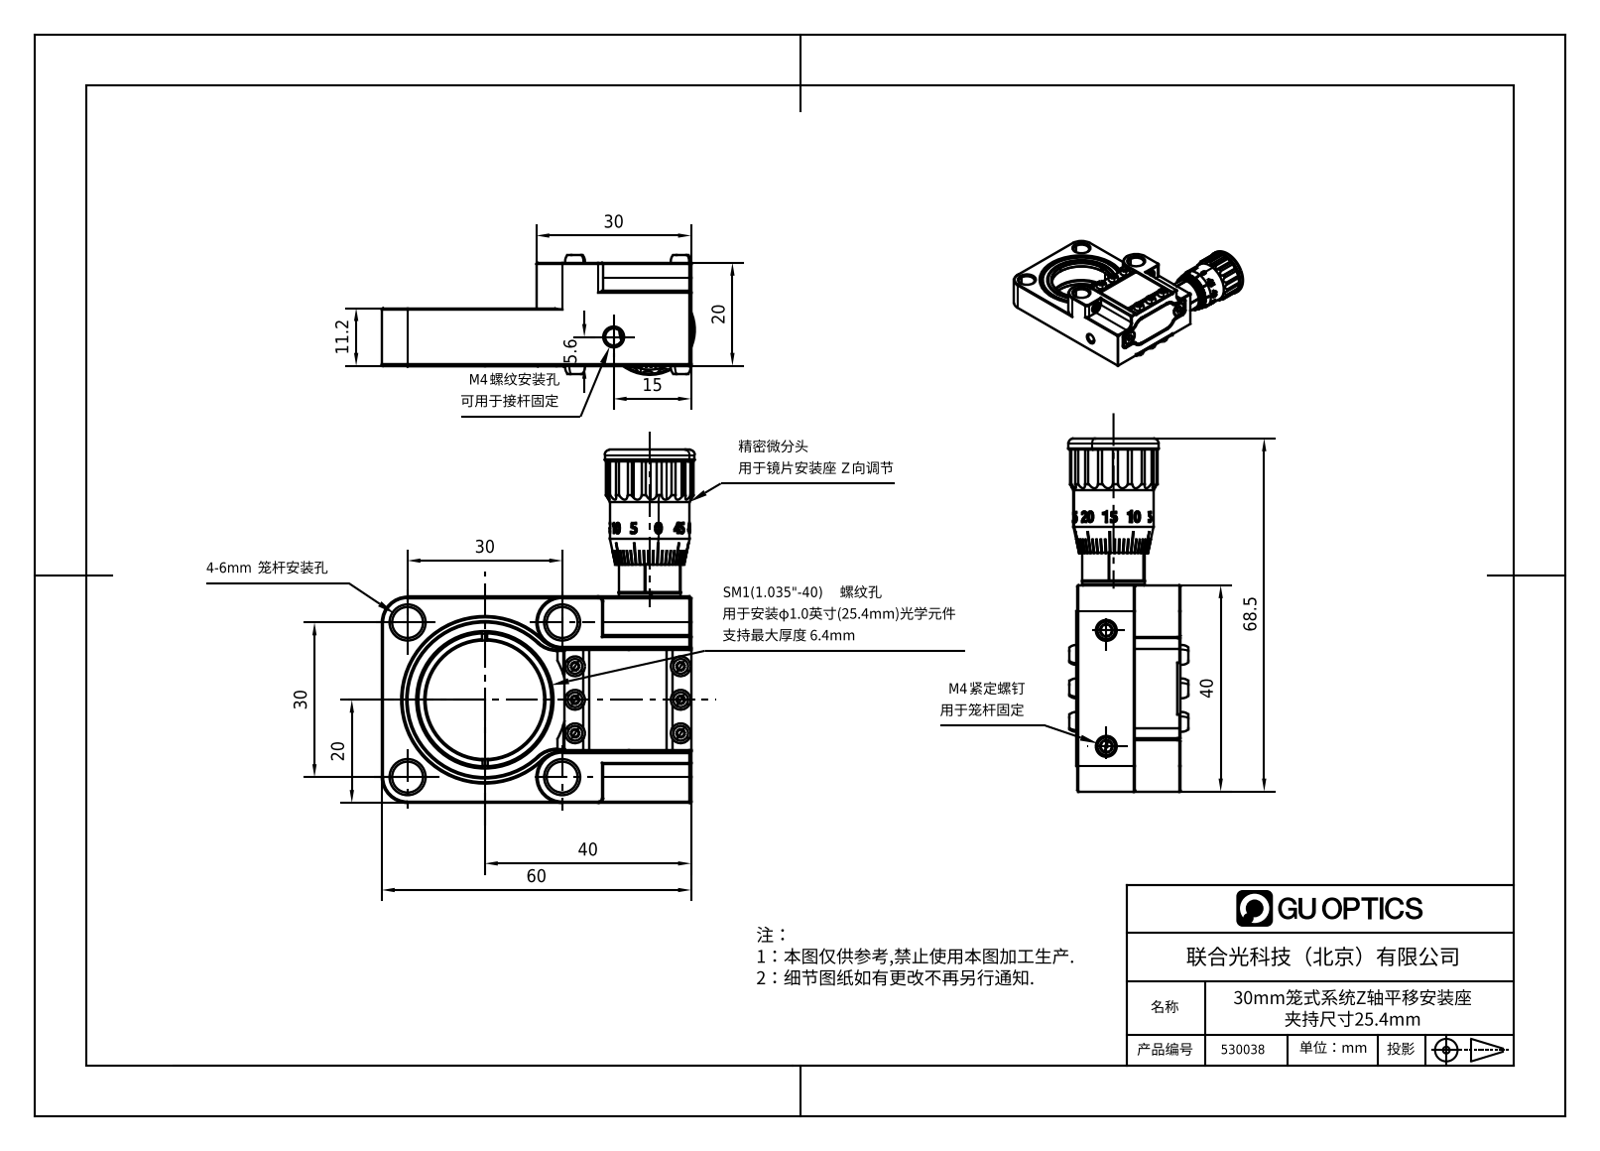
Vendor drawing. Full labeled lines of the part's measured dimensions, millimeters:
STEP written by: SolidWorks 2018 (AUTOMOTIVE_DESIGN)
Units: millimetres
Bodies: 0 solids, 730 faces (347 planar, 147 cylindrical, 236 other)
Overall size (bounding box): 68.5 × 60.75 × 23.31
Round holes (diameter × count): ⌀6 ×4, ⌀3.3 ×3, ⌀12.2 ×1, ⌀23.01 ×1, ⌀25.65 ×1, ⌀32 ×1
Round bosses / shafts (diameter × count): ⌀26.29 ×1, ⌀17.5 ×1, ⌀15.5 ×1, ⌀12 ×1
Partial cylindrical surfaces — rounded edges, fillets, slot ends (radius × count): R1.5 ×33, R4.2 ×8, R5 ×6, R1 ×2, R2.5 ×2, R5.5 ×2, R5.99 ×1, R7.74 ×1
Main face-to-face distances: 20, 40, 11.2, 8.8, 10, 30, 60, 10.25, 29.75, 19.75
Hole centre spacings: 30, 21.21, 42.43, 7.14
